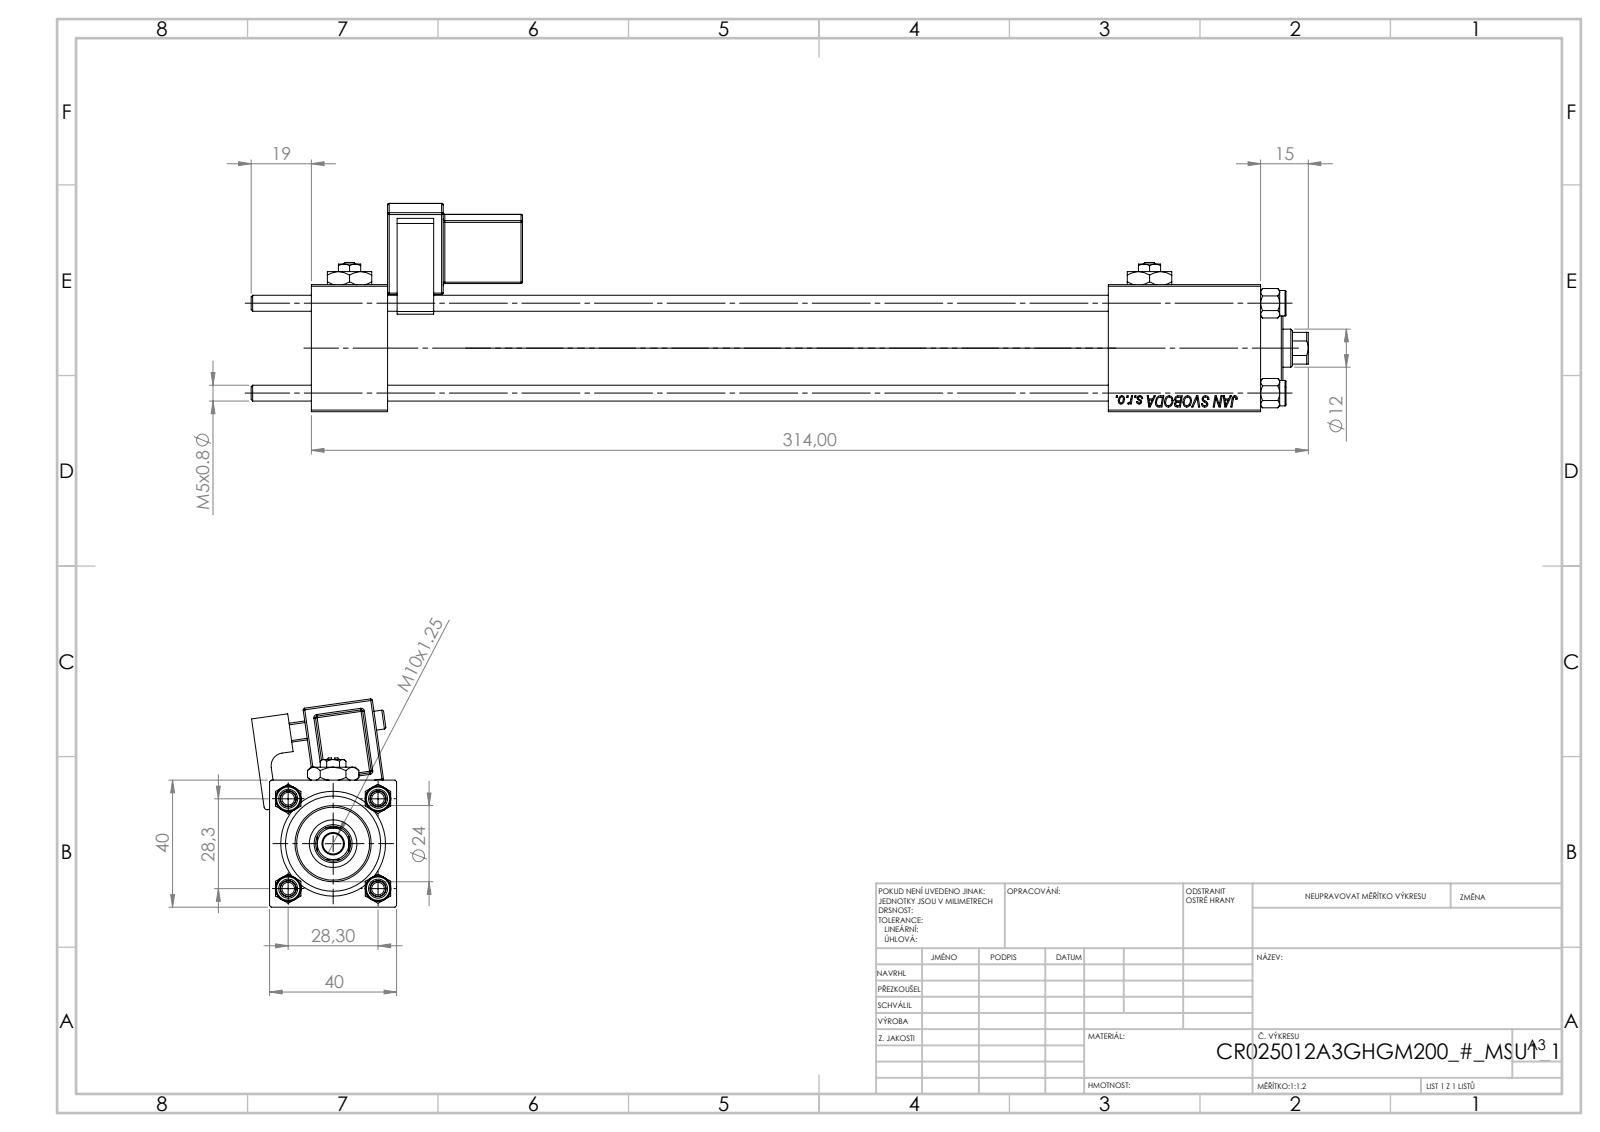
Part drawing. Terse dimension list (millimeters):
name: V215_VC_A; V215CR_VCP; V215CR_MSU; Zatka_pro_OIL_PORT (+3 more)
written by: SolidWorks 2019 (CONFIG_CONTROL_DESIGN)
unit: mm
bodies: 14 solids, 1311 faces (595 planar, 120 cylindrical, 596 other)
size: 333 × 65.59 × 45.69
volume: 245 699 mm³; area: 116 381 mm²
holes: 4× ⌀5, 3× ⌀20, 2× ⌀7, 2× ⌀13.16, 1× ⌀6.5, 1× ⌀12, 1× ⌀15, 1× ⌀25, 1× ⌀30
bosses: 4× ⌀8, 1× ⌀31, 1× ⌀24, 1× ⌀6
rounds: 24× R0.5, 1× R1, 1× R2.5, 1× R4, 1× R5.5
face distances: 40, 24, 3, 39.8, 299, 275, 270.3, 246.3, 28.7, 251
hole spacings: 20.01, 28.3, 40.02, 252
